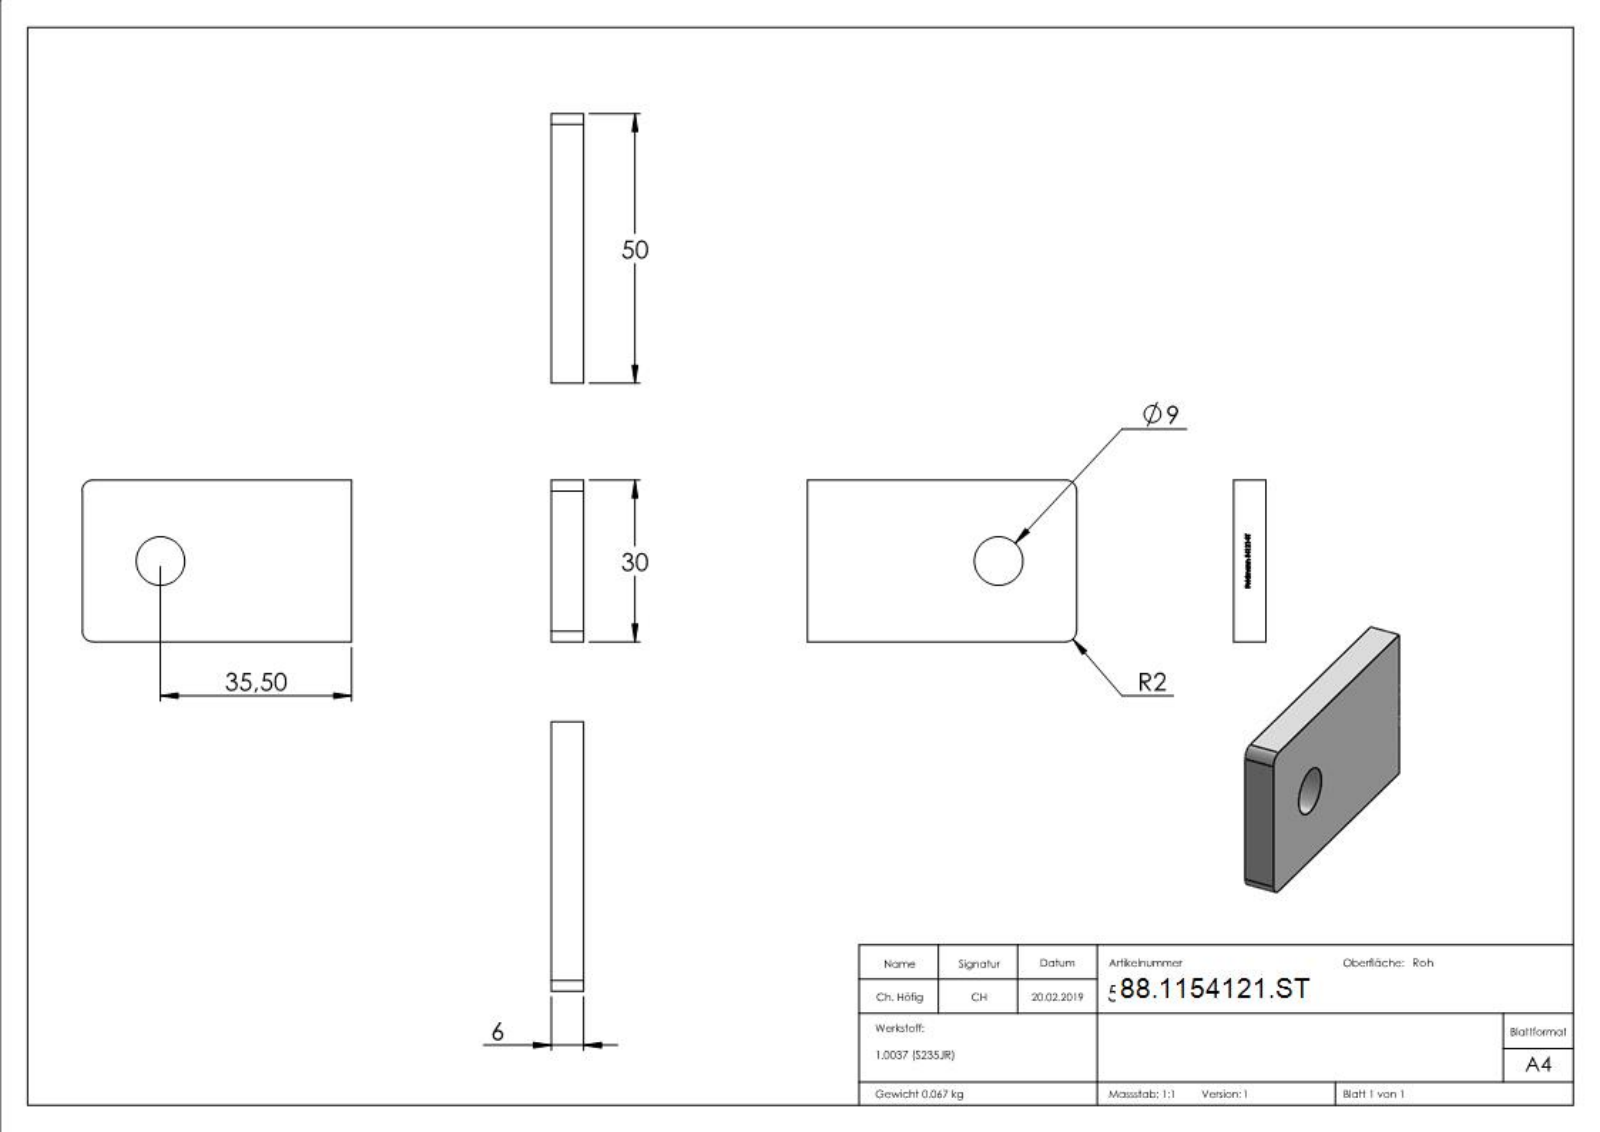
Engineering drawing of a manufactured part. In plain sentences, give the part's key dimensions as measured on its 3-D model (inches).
The part is named "54121-ST". Its 3-D file was written by "SolidWorks 2015 (CONFIG_CONTROL_DESIGN)". It is 1 solid with 212 faces: 131 planar, 4 cylindrical and 77 other. Overall it measures 1.969 by 1.181 by 0.236 inches. Its volume is 0.525 cubic inches and its surface area 6.191 square inches. Round holes: 1 of diameter 0.354. Partial cylindrical surfaces (rounded edges, fillets, slot ends): 2 of radius 0.079. The main face-to-face distances are 0.236, 1.181, 1.969, 1.965, 0.118, 0.028, 0.23, 0.278, 0.048, 0.048.
